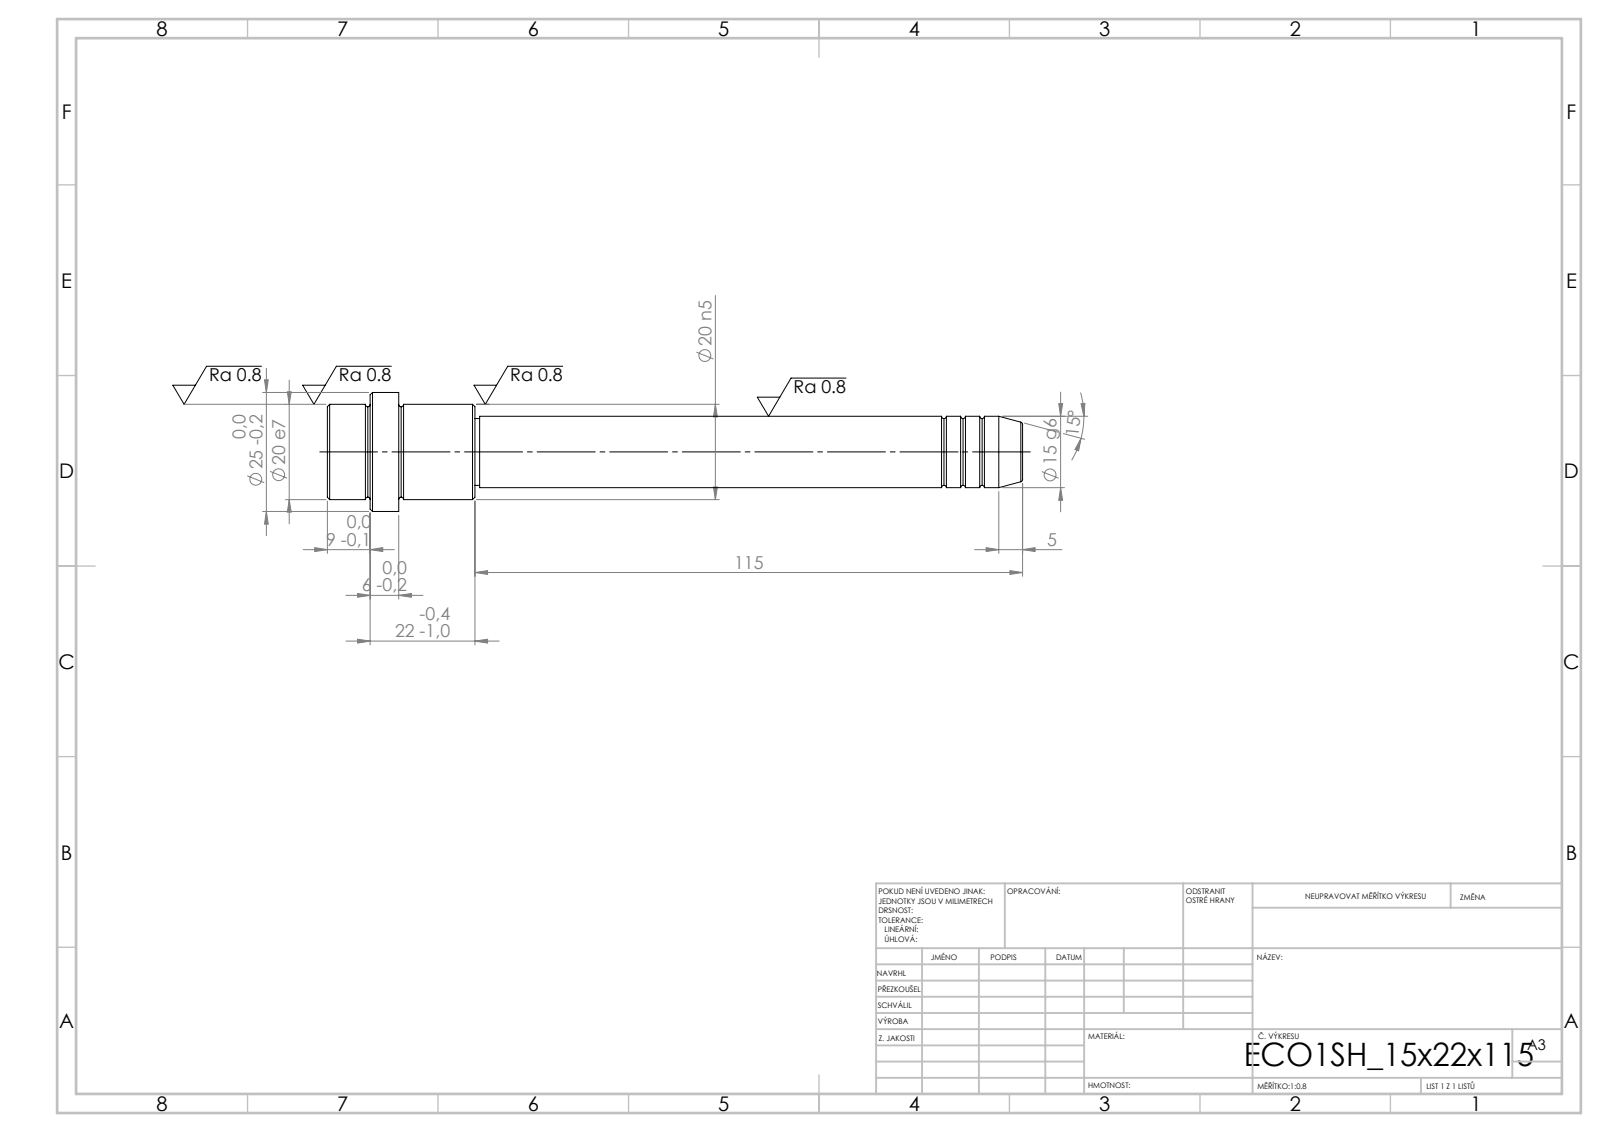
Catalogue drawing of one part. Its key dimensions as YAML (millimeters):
step_written_by: "SolidWorks 2019 (CONFIG_CONTROL_DESIGN)"
units: millimeters
bodies: {solids: 1, faces: 52, planar: 6, cylindrical: 16, other: 30}
overall_size: [146, 25, 25]
volume: 30822
surface_area: 8486
round_bosses_or_shafts:
  - {diameter: 25, count: 1}
  - {diameter: 20, count: 1}
  - {diameter: 15, count: 1}
  - {diameter: 14, count: 1}
face_to_face_distances: [15, 6, 9, 16, 22, 31, 115, 131, 137, 146]
